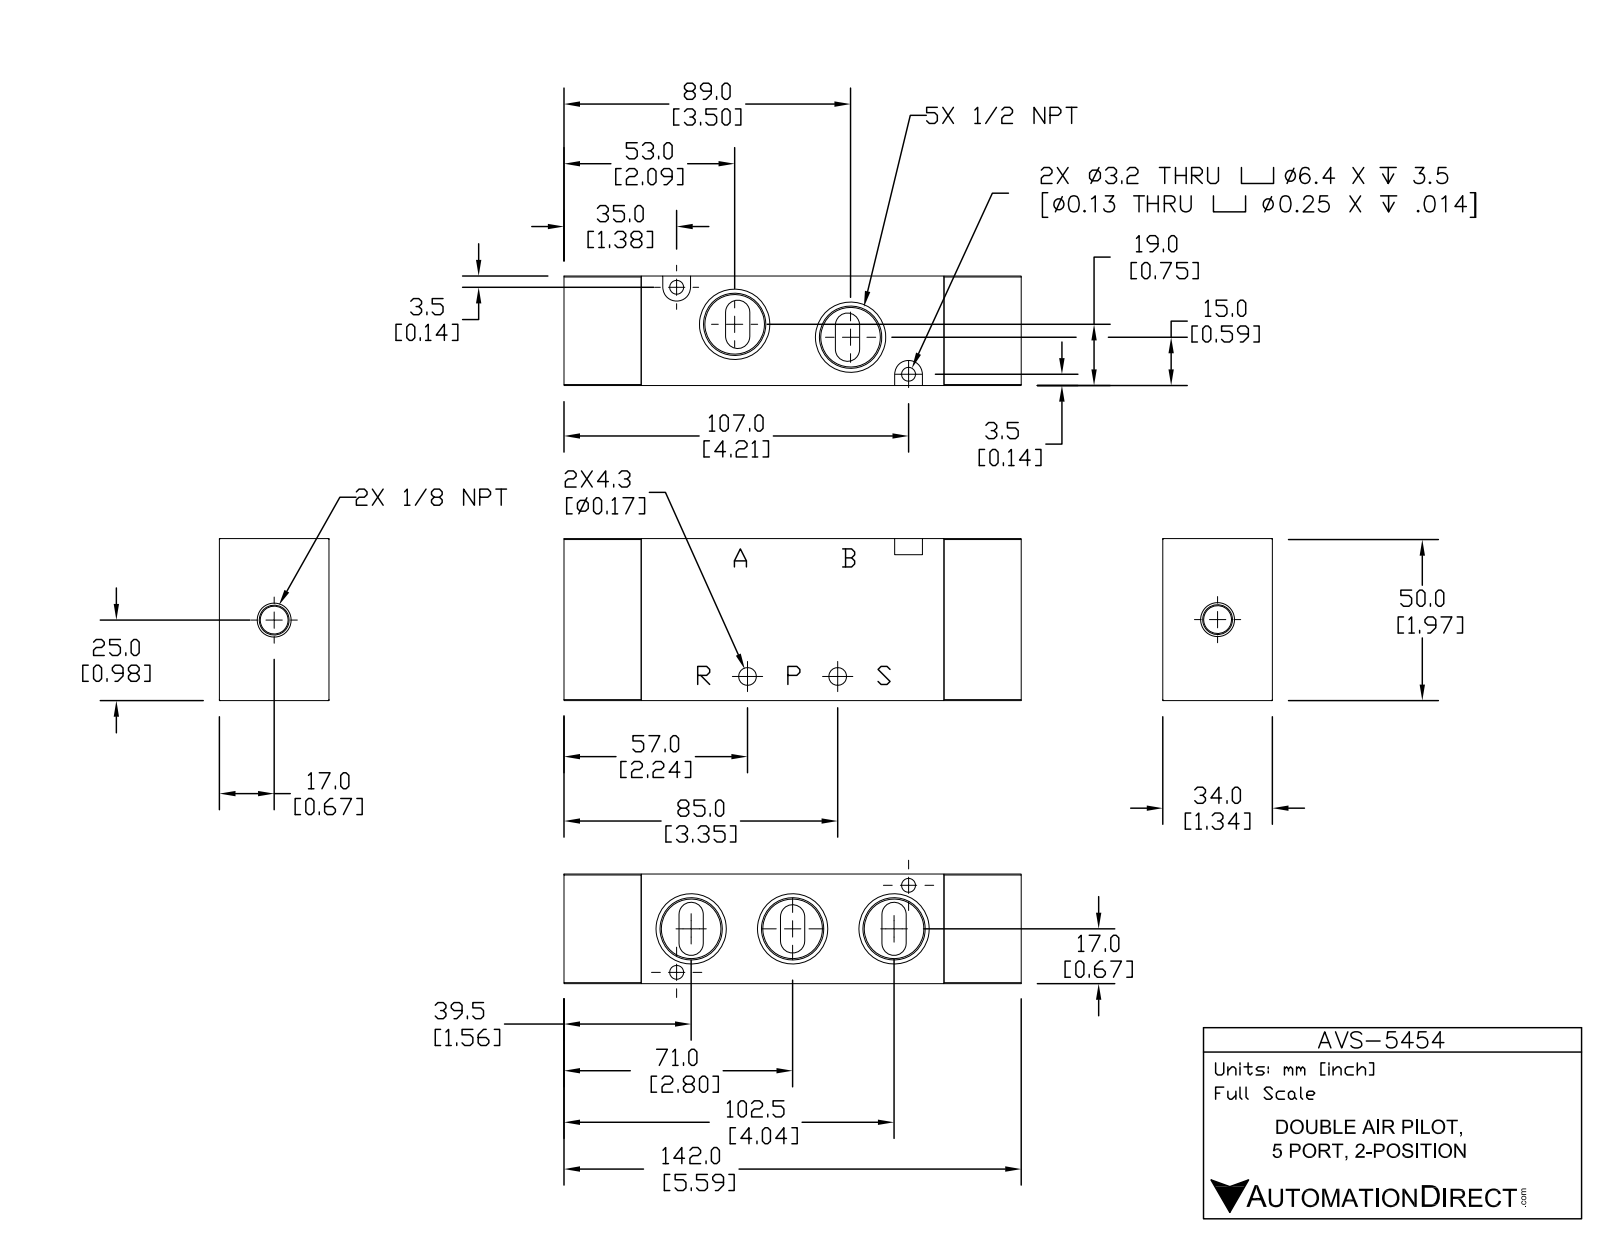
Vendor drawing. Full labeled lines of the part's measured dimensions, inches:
Part name (STEP PRODUCT): AVS-5454
STEP written by: SolidWorks 2015 (CONFIG_CONTROL_DESIGN)
Units: inches
Bodies: 3 solids, 108 faces (46 planar, 34 cylindrical, 28 other)
Overall size (bounding box): 5.591 × 1.969 × 1.339
Volume: 12.98 in³ · Surface area: 65.18 in²
Round holes (diameter × count): ⌀0.169 ×2, ⌀0.217 ×2
Partial cylindrical surfaces — rounded edges, fillets, slot ends (radius × count): R0.148 ×10, R0.012 ×4, R0.169 ×2
Main face-to-face distances: 1.339, 1.969, 3.701, 0.945, 4.646, 5.591, 0.579, 1.389, 0.787, 1.181
Hole centre spacings: 1.102, 3.028
